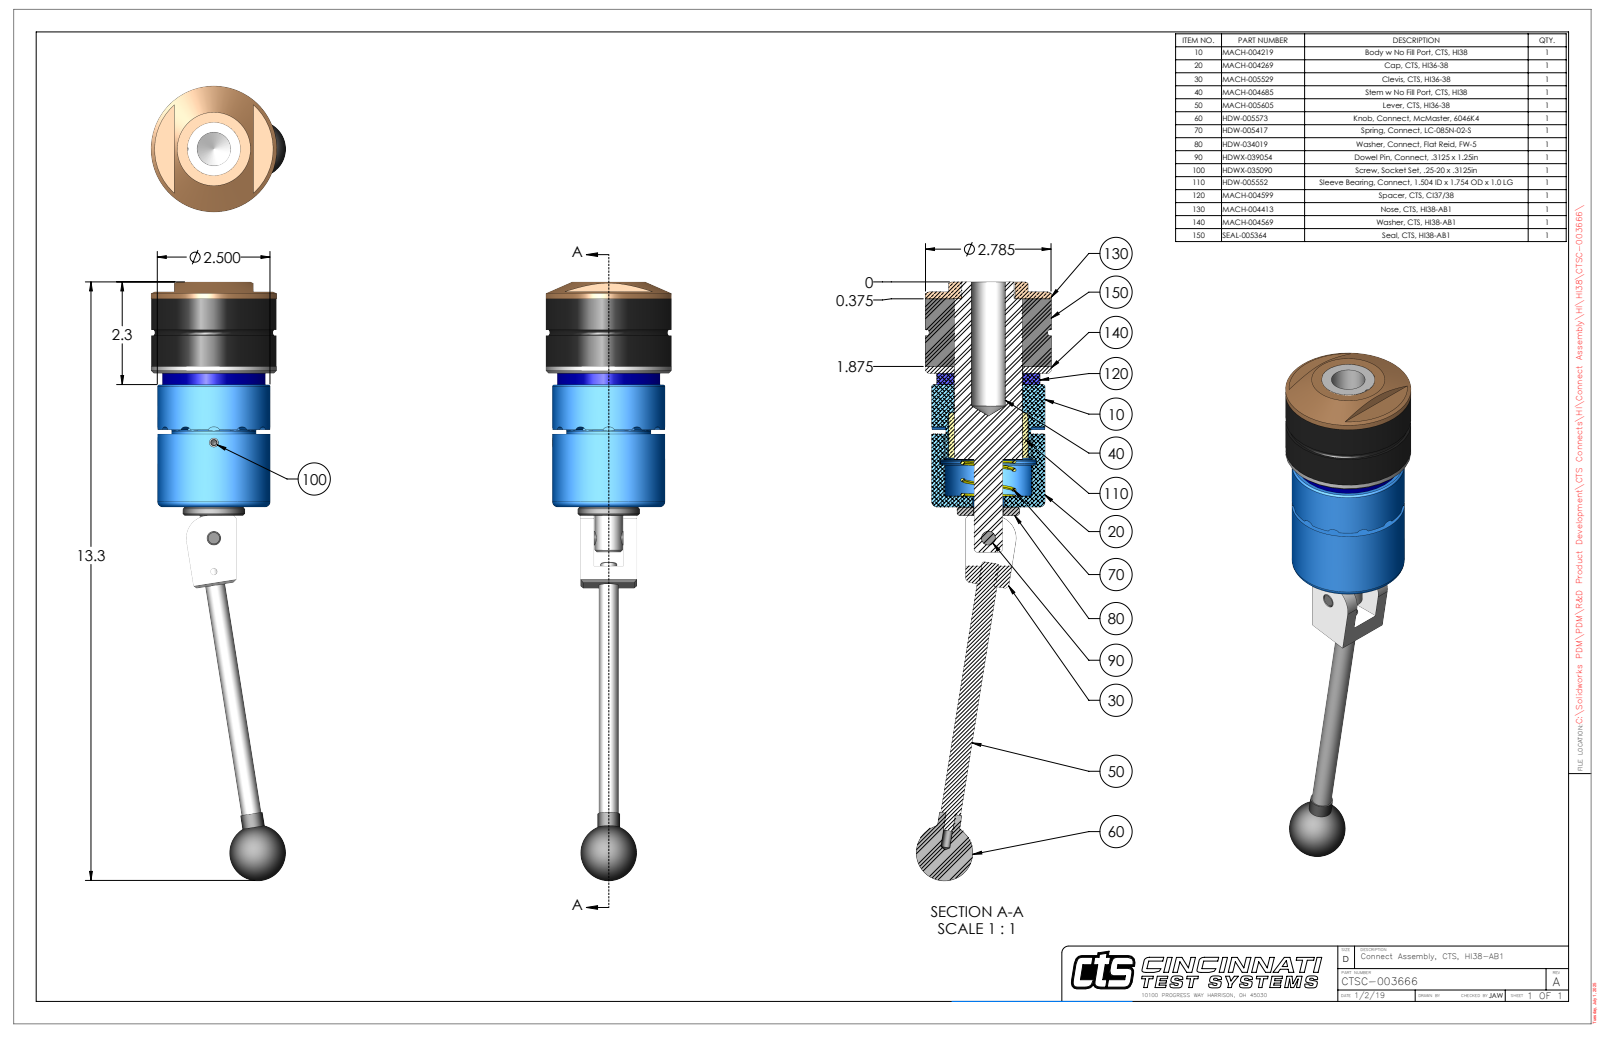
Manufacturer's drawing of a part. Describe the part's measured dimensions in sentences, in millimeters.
The part is named "CTSC-003666". Its 3-D file was written by "SolidWorks 2023 (AUTOMOTIVE_DESIGN)". It is 10 solids with 274 faces: 98 planar, 107 cylindrical and 69 other. Overall it measures 337.2 by 75.8 by 70.7 millimeters. Its volume is 459 500 cubic millimeters and its surface area 95 480 square millimeters. Round holes: 1 of diameter 3.8, 1 of diameter 5.1, 1 of diameter 7.9, 1 of diameter 8, 1 of diameter 8, 1 of diameter 16.7, 1 of diameter 17.7, 1 of diameter 19.1, 1 of diameter 29.8, 1 of diameter 38, 1 of diameter 38.1, 1 of diameter 38.4. Round bosses or shafts: 1 of diameter 70.7, 1 of diameter 70.7, 1 of diameter 63.5, 1 of diameter 57.9, 1 of diameter 47.6, 1 of diameter 38.1, 1 of diameter 38, 1 of diameter 35.1. Partial cylindrical surfaces (rounded edges, fillets, slot ends): 12 of radius 3, 2 of radius 0.7, 1 of radius 2.6, 1 of radius 12.7, 1 of radius 31.1. The main face-to-face distances are 38.1, 3.9, 42, 6.4, 10.2, 48.3, 68.9, 75.3, 79.1, 117.2. The hole center spacings are 18.8.
